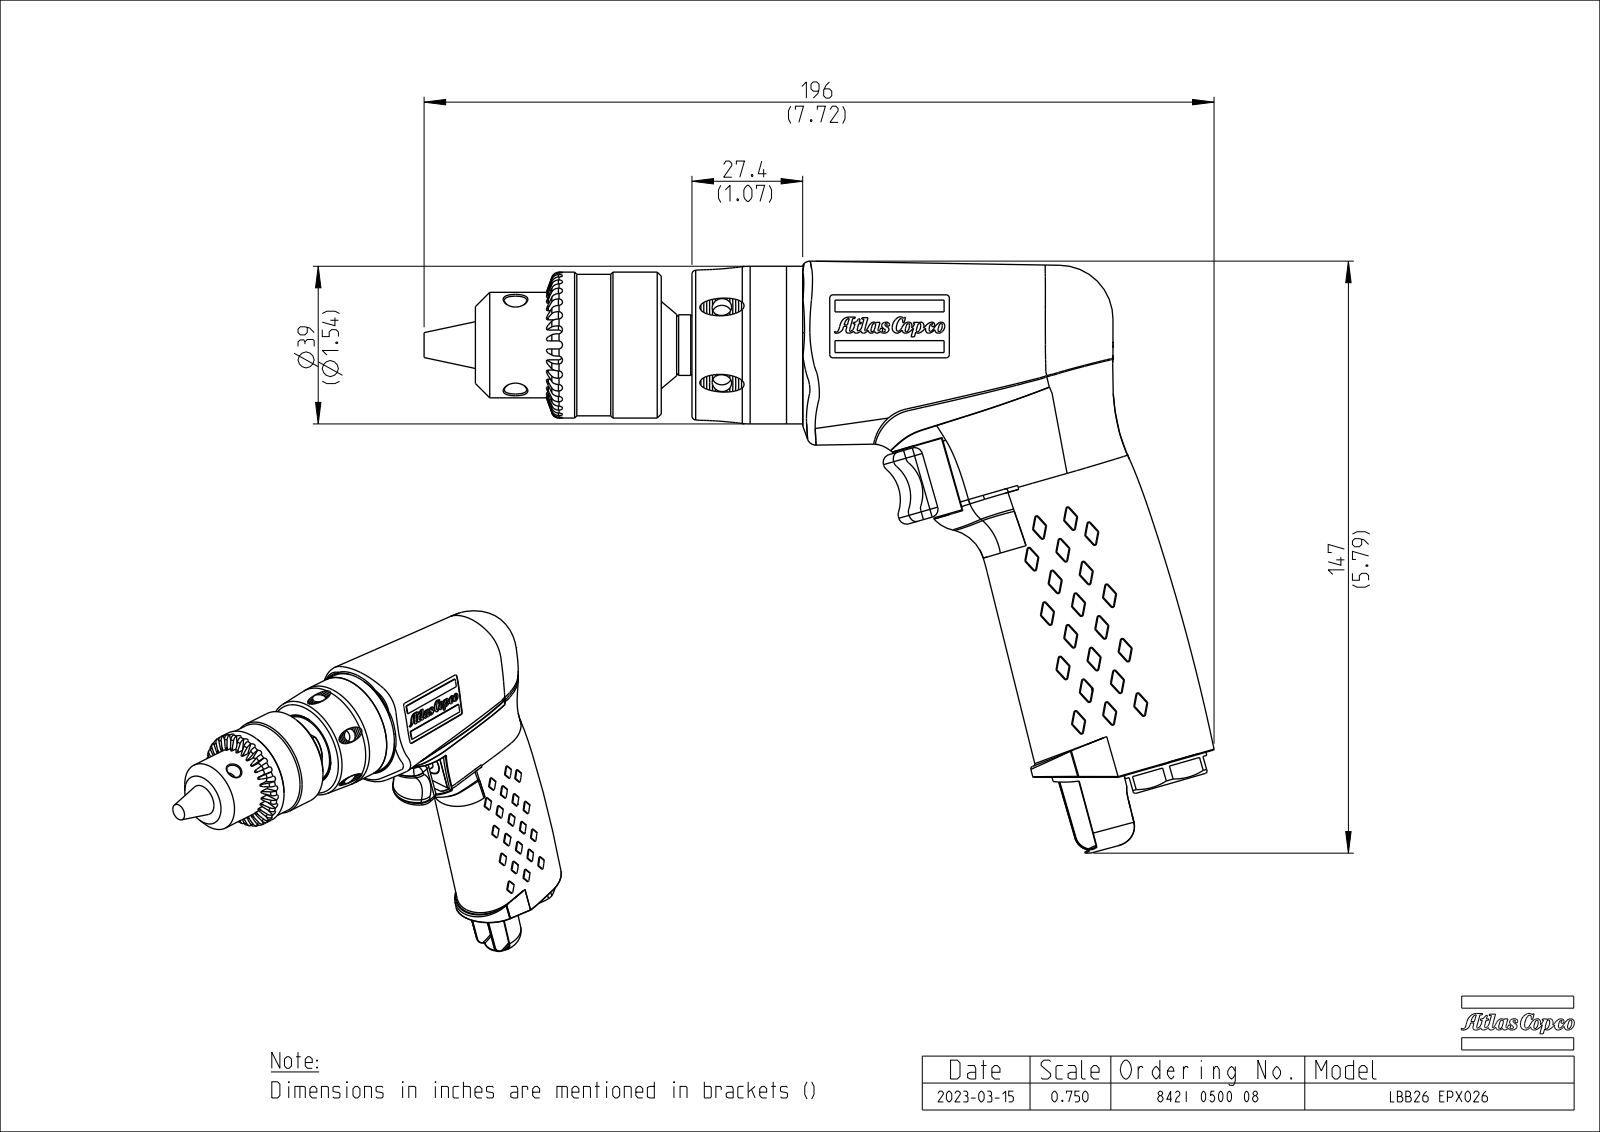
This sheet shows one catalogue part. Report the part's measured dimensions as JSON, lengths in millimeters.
{"part_name": "EXT_COMP_SW0002", "step_written_by": "CREO PARAMETRIC BY PTC INC, 2020281 (CONFIG_CONTROL_DESIGN)", "units": "millimeters", "bodies": {"solids": 1, "faces": 3316, "planar": 393, "cylindrical": 203, "other": 2720}, "overall_size": [195.5, 146.4, 48.1], "volume_mm3": 235000, "surface_area_mm2": 77740, "round_holes": [[4.8, 3], [5.5, 3], [11.8, 1], [12.4, 1], [17.5, 1], [18.5, 1], [35.8, 1]], "round_bosses_or_shafts": [[39, 1], [37, 1], [36.1, 1], [35, 1], [26.1, 1], [21, 1], [12, 1], [9.8, 1]], "partial_cylinders_radius": [[0.5, 60], [1, 30], [0.2, 14], [2, 8], [0.3, 7], [0.8, 4], [0.3, 2], [0.3, 2]], "face_to_face_distances": [7.6, 9.2, 35, 27.4, 2, 92.7, 81, 53.6, 46, 5.6]}
